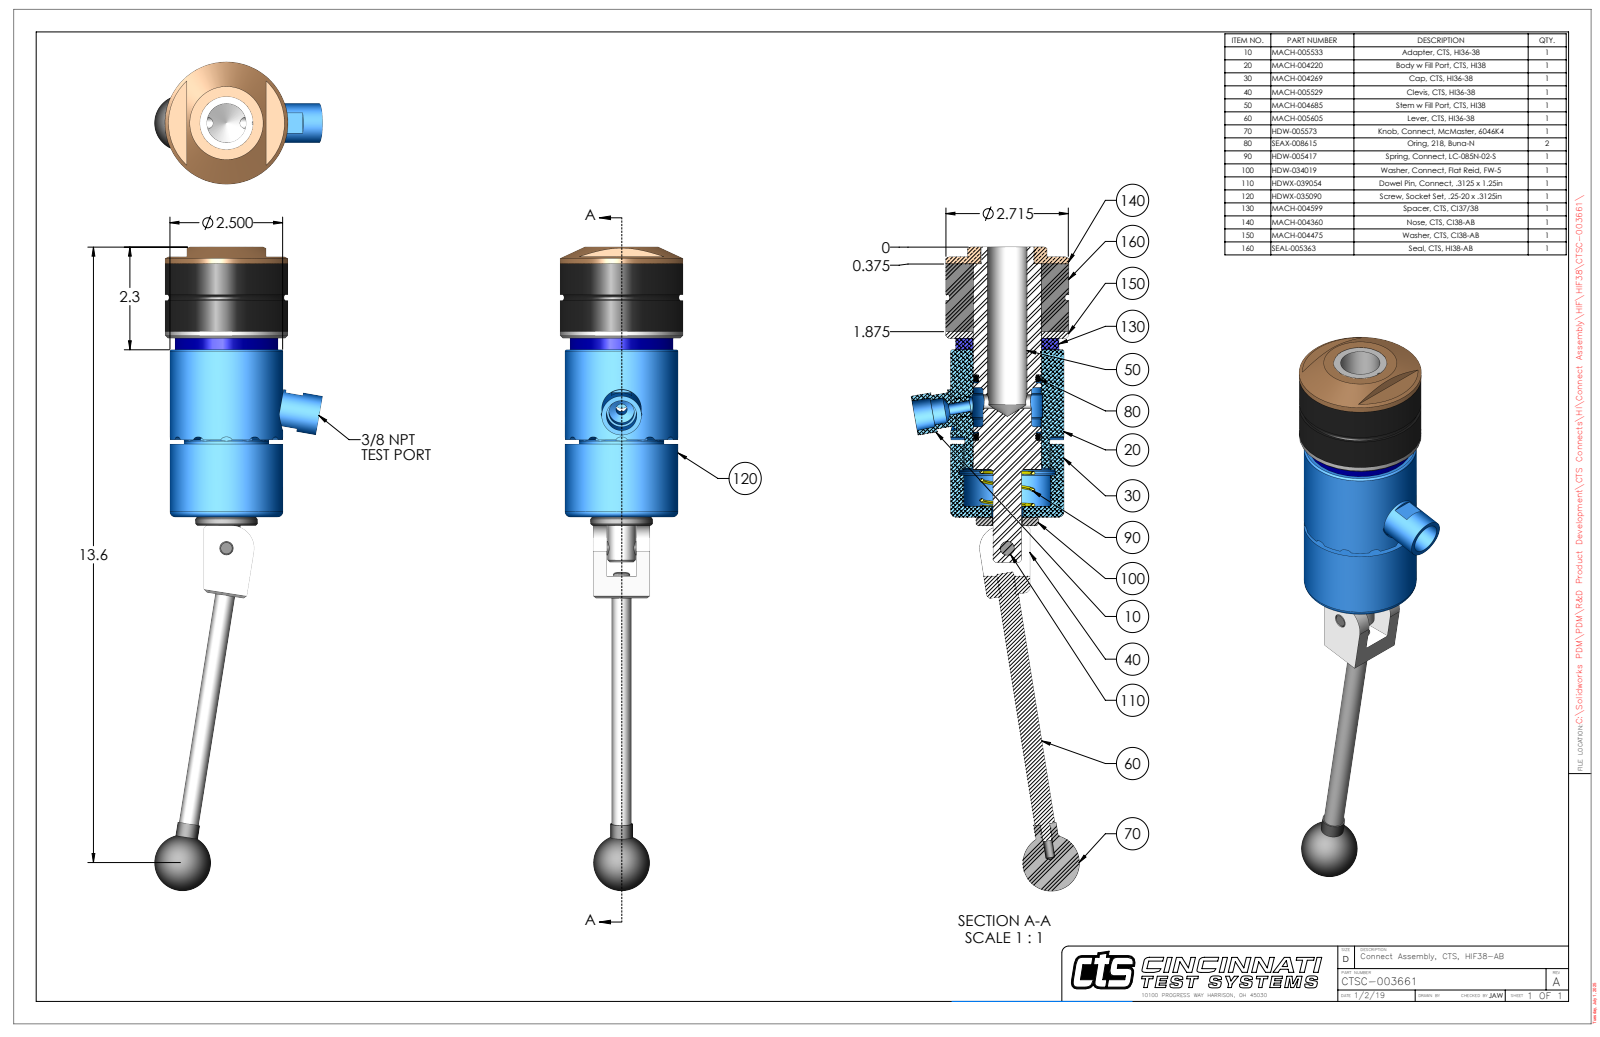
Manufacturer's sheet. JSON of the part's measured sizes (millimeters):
{"part_name": "CTSC-003661", "step_written_by": "SolidWorks 2023 (AUTOMOTIVE_DESIGN)", "units": "millimeters", "bodies": {"solids": 10, "faces": 316, "planar": 111, "cylindrical": 130, "other": 75}, "overall_size": [362.6, 94.4, 69], "volume_mm3": 520100, "surface_area_mm2": 102300, "round_holes": [[5.1, 2], [3.8, 1], [6.4, 1], [7.9, 1], [7.9, 1], [8, 1], [8, 1], [14.3, 1], [16.7, 1], [17.7, 1], [22.2, 1], [29.8, 1]], "round_bosses_or_shafts": [[69, 1], [63.5, 1], [57.9, 1], [47.6, 1], [38.1, 1], [38, 1], [35.1, 1], [31.8, 1]], "partial_cylinders_radius": [[3, 12], [0.7, 2], [4.8, 1], [5, 1], [11.9, 1], [11.9, 1], [12.7, 1], [30.4, 1]], "face_to_face_distances": [38.1, 3.9, 42, 6.4, 10.2, 48.3, 94.3, 100.7, 104.5, 142.6], "hole_center_spacings": [18.8, 53.8, 72.6]}
